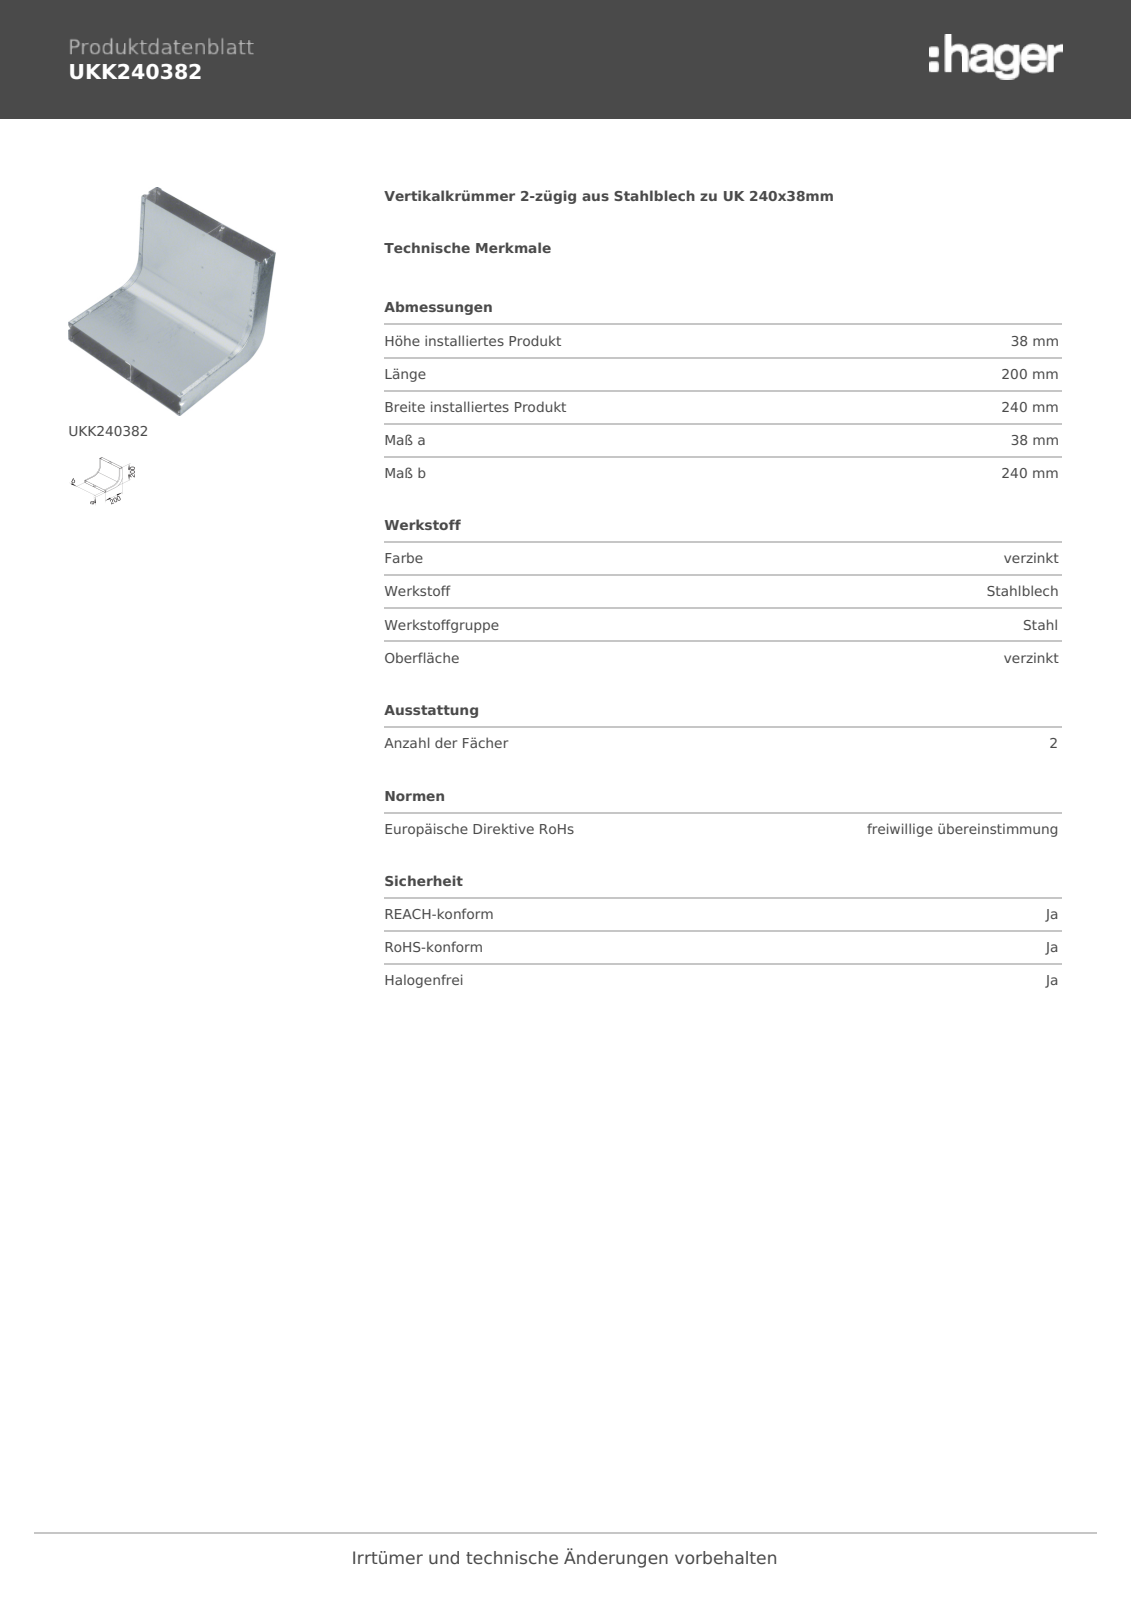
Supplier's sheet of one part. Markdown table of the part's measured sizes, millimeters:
| quantity | value |
| --- | --- |
| part name | UKKI_240-38-SIMPLIFIED; UKKS_38-SIMPLIFIED; UKKA_240-SIMPLIFIED; UKKT_38-SIMPLIFIED (+1 more) |
| STEP written by | CREO PARAMETRIC BY PTC INC, 2022024 (AUTOMOTIVE_DESIGN) |
| units | millimeters |
| bodies | 5 solids, 62 faces (49 planar, 13 cylindrical, 0 other) |
| overall size | 240 × 200.53 × 200.5 |
| volume | 166 073 mm³ |
| surface area | 446 490 mm² |
| partial cylindrical surfaces (radius × count) | 1 × 5, 1.75 × 3, 0.25 × 1 |
| main face-to-face distances | 0.75, 35.75, 35, 36.5, 239.25, 138.5, 100.75, 240, 238.5, 101.5 |
